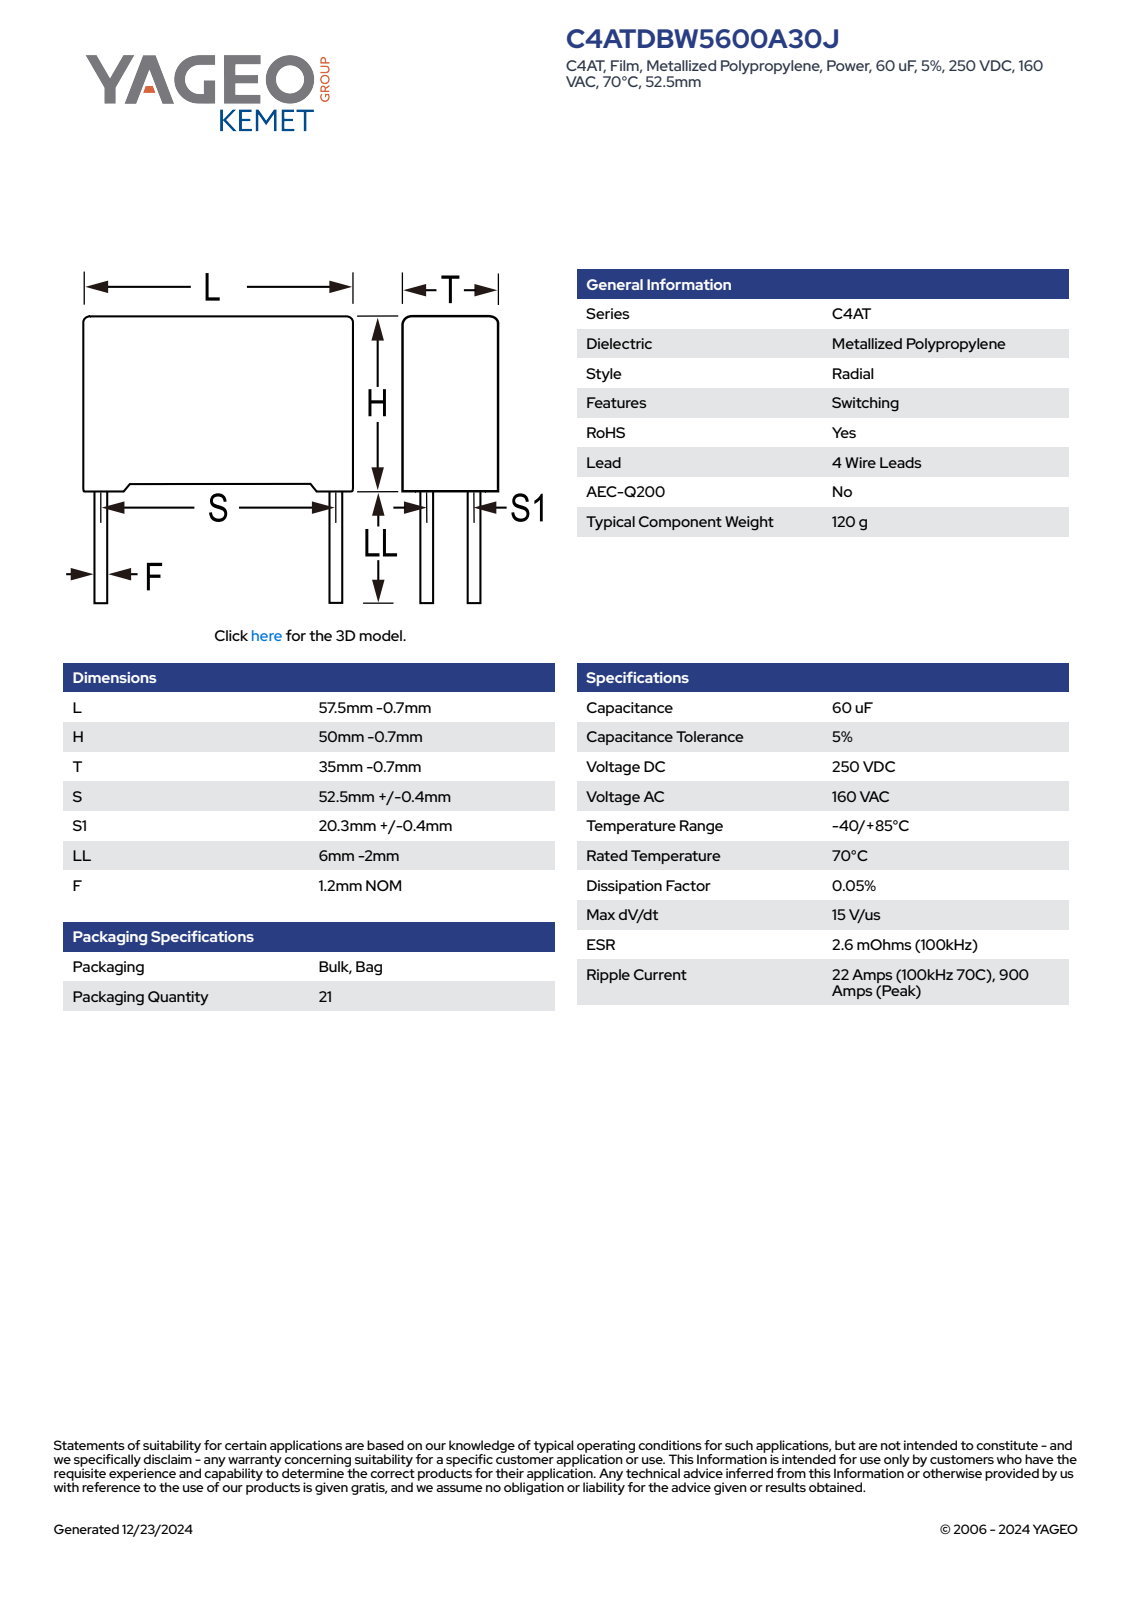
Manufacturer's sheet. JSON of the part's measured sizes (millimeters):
{"part_name": "CFP_RB4_57.5X50X35_L56.8H49.3T34.3S52.5S120.3LL4F1.2", "step_written_by": "SolidWorks 2014 (AUTOMOTIVE_DESIGN)", "units": "millimeters", "bodies": {"solids": 4, "faces": 91, "planar": 83, "cylindrical": 8, "other": 0}, "overall_size": [56.8, 53.3, 34.3], "volume_mm3": 93516, "surface_area_mm2": 13150, "round_bosses_or_shafts": [[1.2, 4]], "face_to_face_distances": [34.3, 47.85, 56.8, 1.45, 49.3, 2.11, 54.69, 52.58, 32.19, 30.08]}
